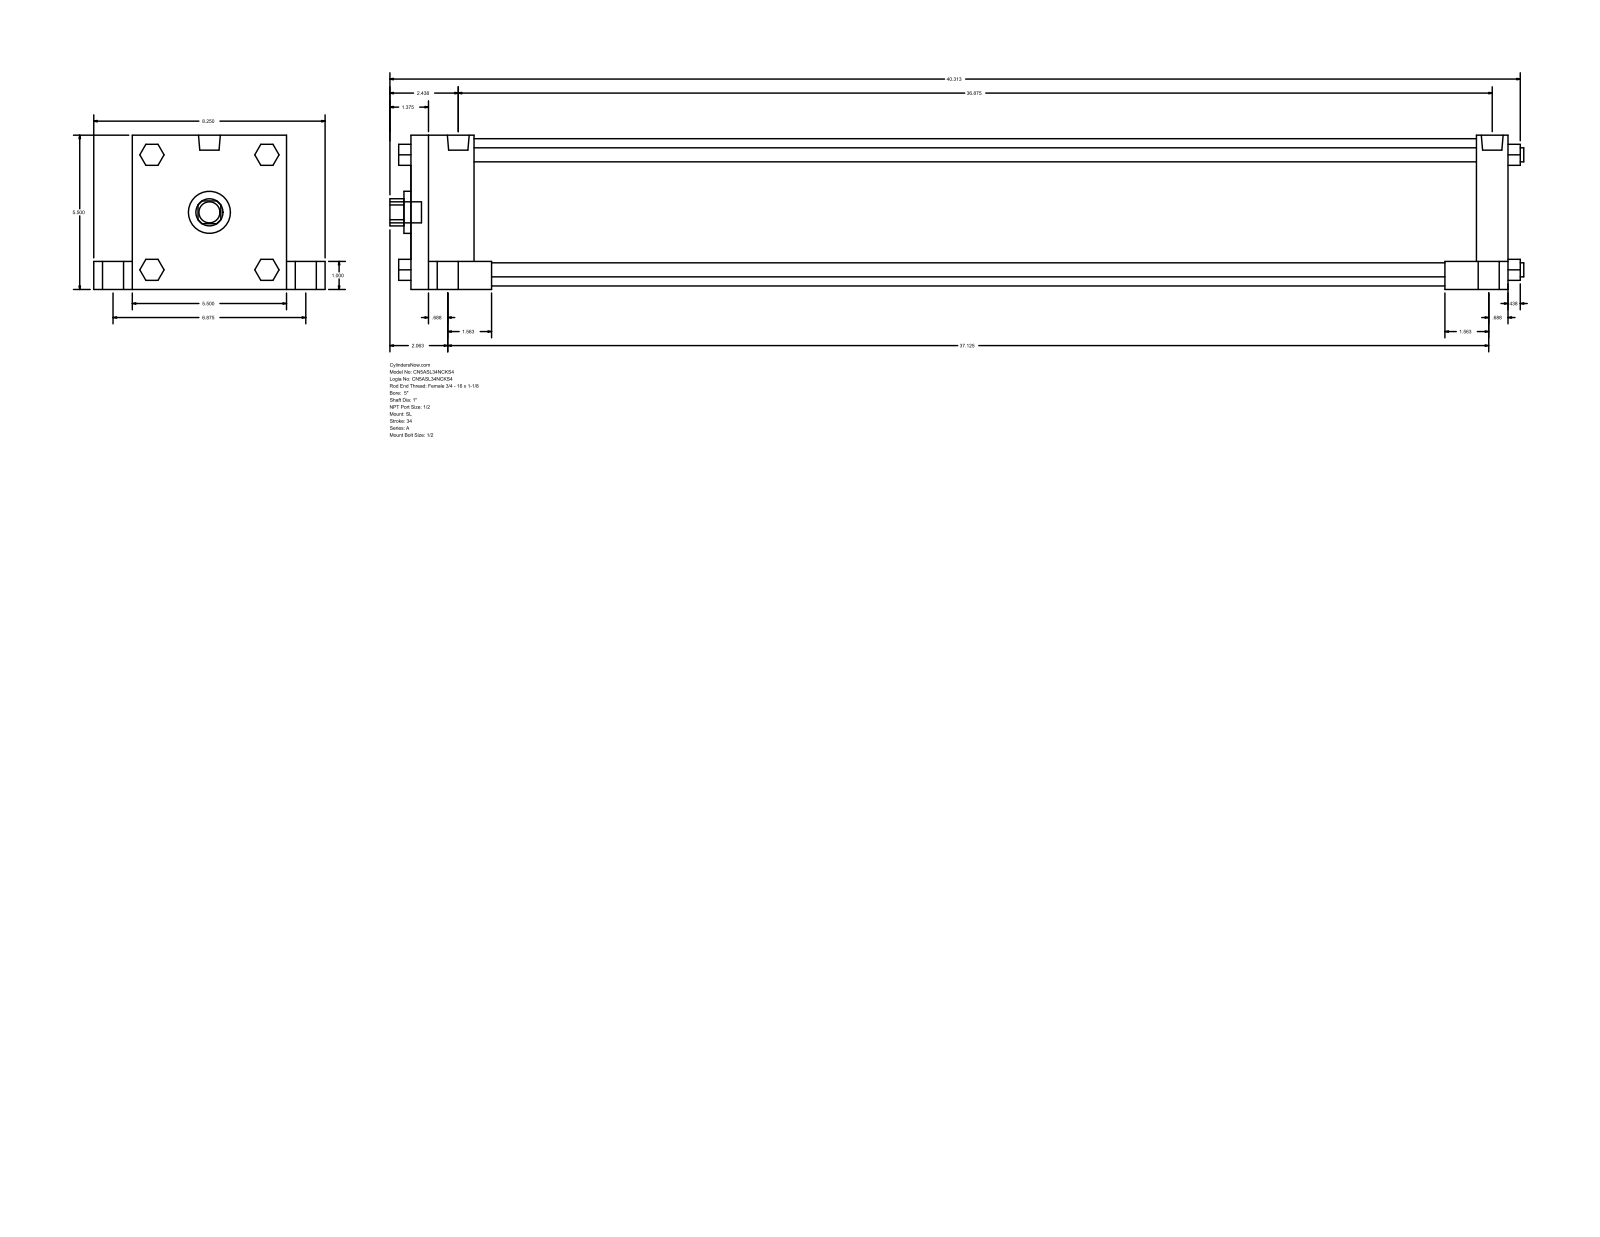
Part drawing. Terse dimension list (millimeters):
name: A_SL__0500_1
written by: GSSL Pune (CONFIG_CONTROL_DESIGN)
unit: mm
bodies: 0 solids, 150 faces (114 planar, 36 cylindrical, 0 other)
size: 1027.11 × 209.55 × 139.7
holes: 1× ⌀25.4, 1× ⌀38.1, 1× ⌀133.35
bosses: 5× ⌀19.05, 4× ⌀25.4, 4× ⌀12.7, 4× ⌀8.73, 2× ⌀19.77
rounds: 1× R12.29
face distances: 139.7, 993.78, 28.58, 25.4, 114.3, 34.93, 174.63, 57.15, 965.2, 908.05
